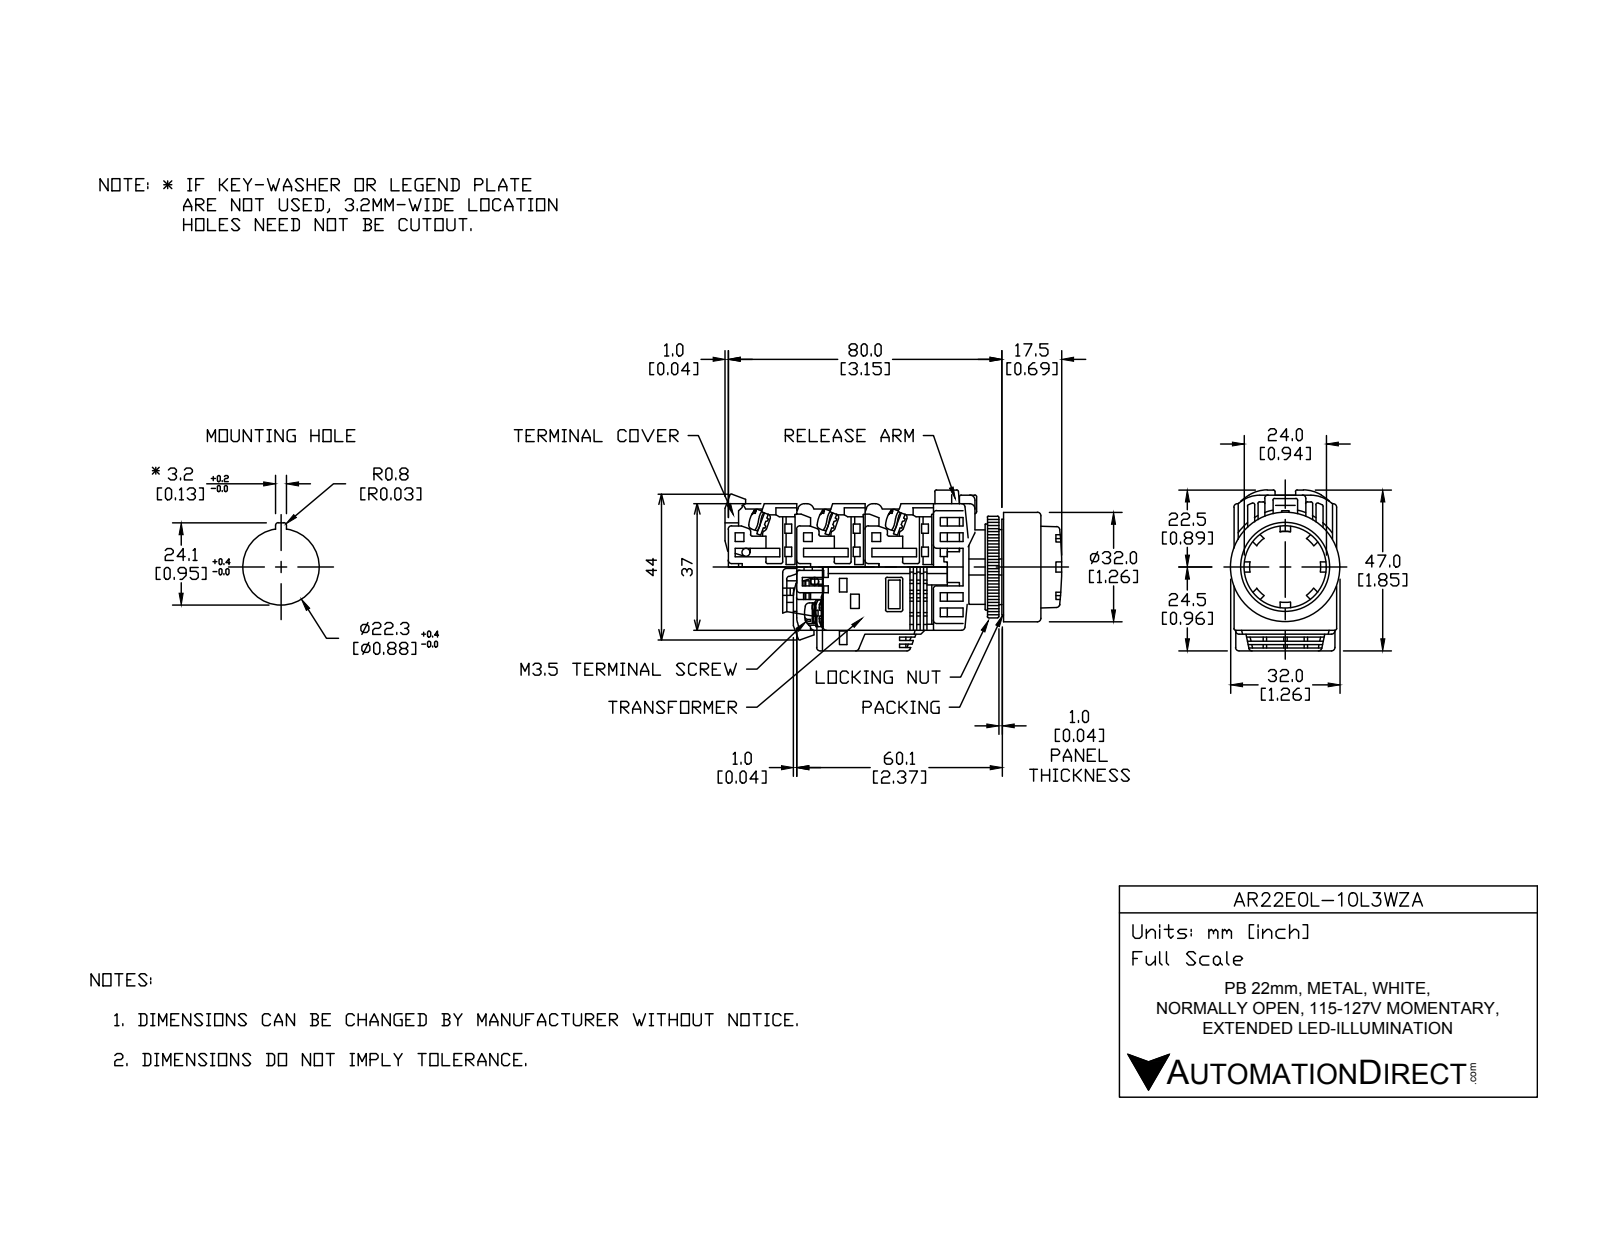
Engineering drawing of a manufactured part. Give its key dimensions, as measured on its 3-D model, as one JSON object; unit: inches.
{"part_name": "AR22E0L-10L3WZA", "step_written_by": "SolidWorks 2017 (AUTOMOTIVE_DESIGN)", "units": "inches", "bodies": {"solids": 16, "faces": 451, "planar": 317, "cylindrical": 99, "other": 35}, "overall_size": [3.12, 1.725, 1.26], "volume_in3": 3.076, "surface_area_in2": 40.62, "round_holes": [[0.858, 1], [0.866, 1], [0.984, 1], [1.22, 1]], "round_bosses_or_shafts": [[0.197, 4], [1.26, 1], [1.201, 1], [1.173, 1], [0.945, 1], [0.937, 1], [0.856, 1], [0.669, 1]], "partial_cylinders_radius": [[0.02, 32], [0.069, 8], [0.197, 4], [0.157, 2], [0.653, 1], [0.693, 1]], "face_to_face_distances": [0.039, 0.709, 1.142, 0.787, 1.122, 0.118, 0.079, 0.827, 0.014, 0.295]}
